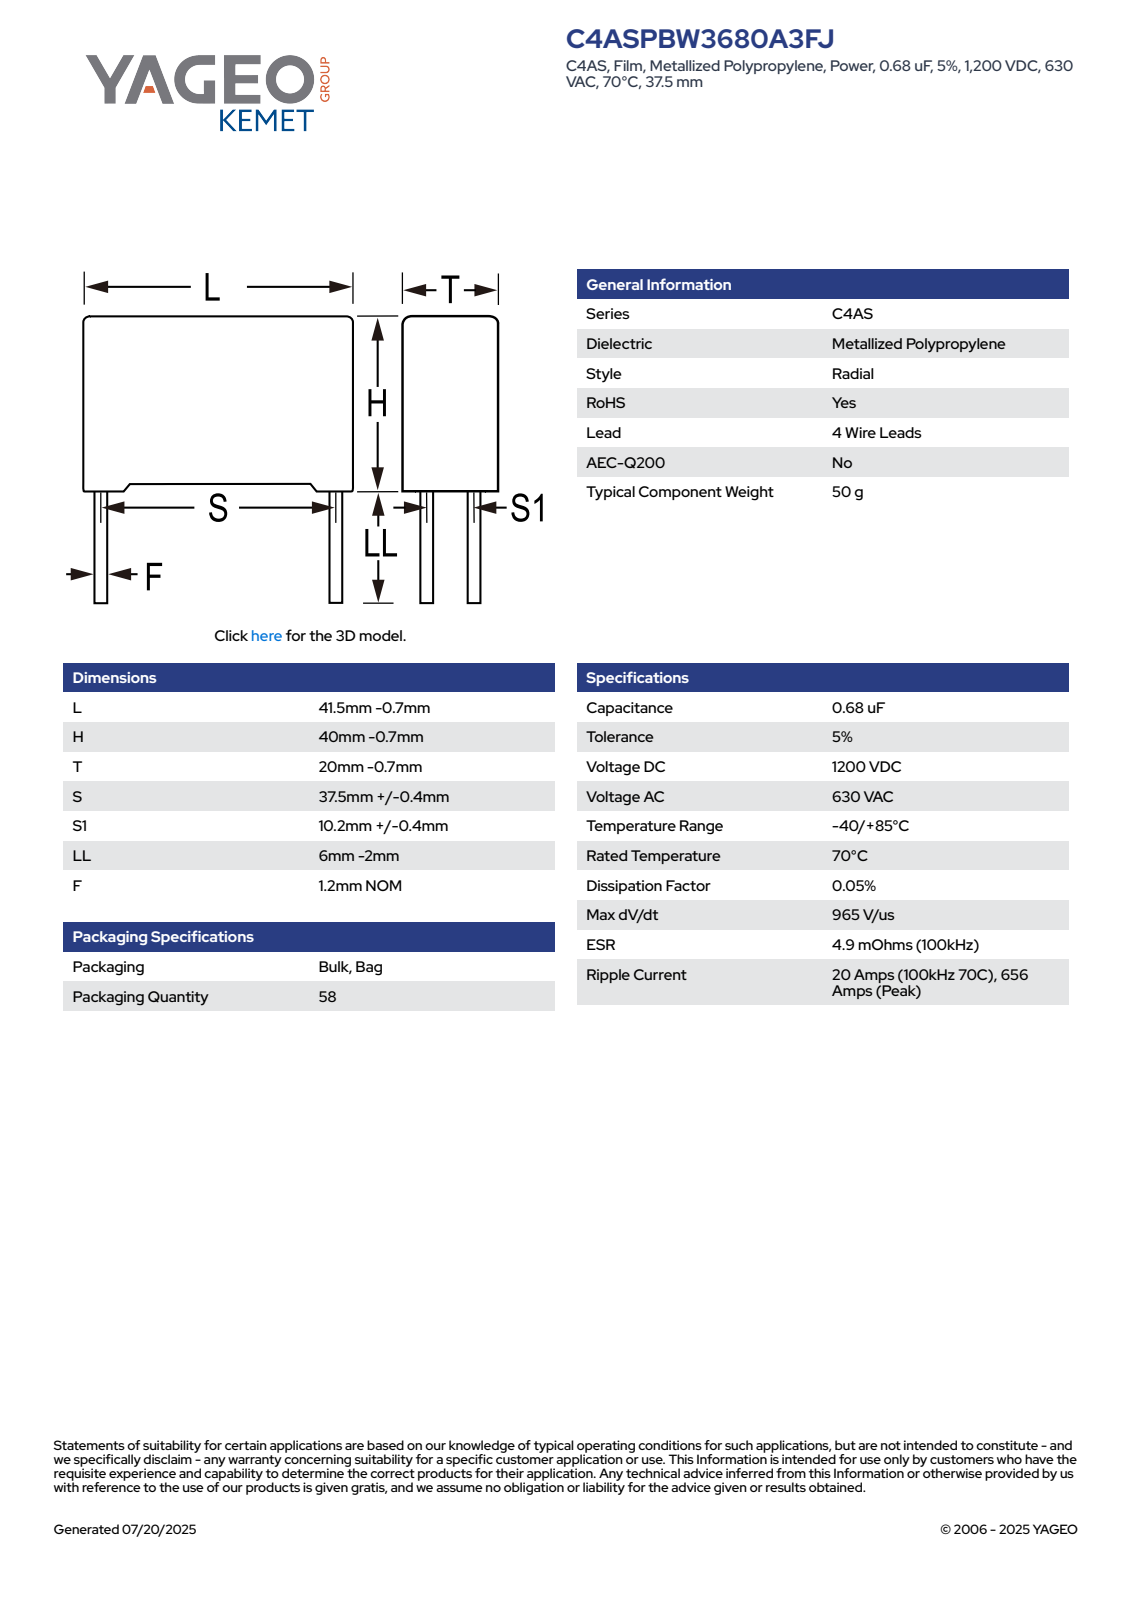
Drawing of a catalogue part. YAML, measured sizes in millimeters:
part_name: "CFP_RB4_41.5X40X20_L40.8H39.3T19.3S37.5S110.2LL4F1.2"
step_written_by: "SolidWorks 2014 (AUTOMOTIVE_DESIGN)"
units: millimeters
bodies: {solids: 4, faces: 91, planar: 83, cylindrical: 8, other: 0}
overall_size: [43.3, 40.8, 19.3]
volume: 30142
surface_area: 6479
round_bosses_or_shafts:
  - {diameter: 1.2, count: 4}
face_to_face_distances: [19.3, 40.8, 38.14, 1.16, 39.3, 1.19, 19.31, 39.61, 18.11, 38.42]
